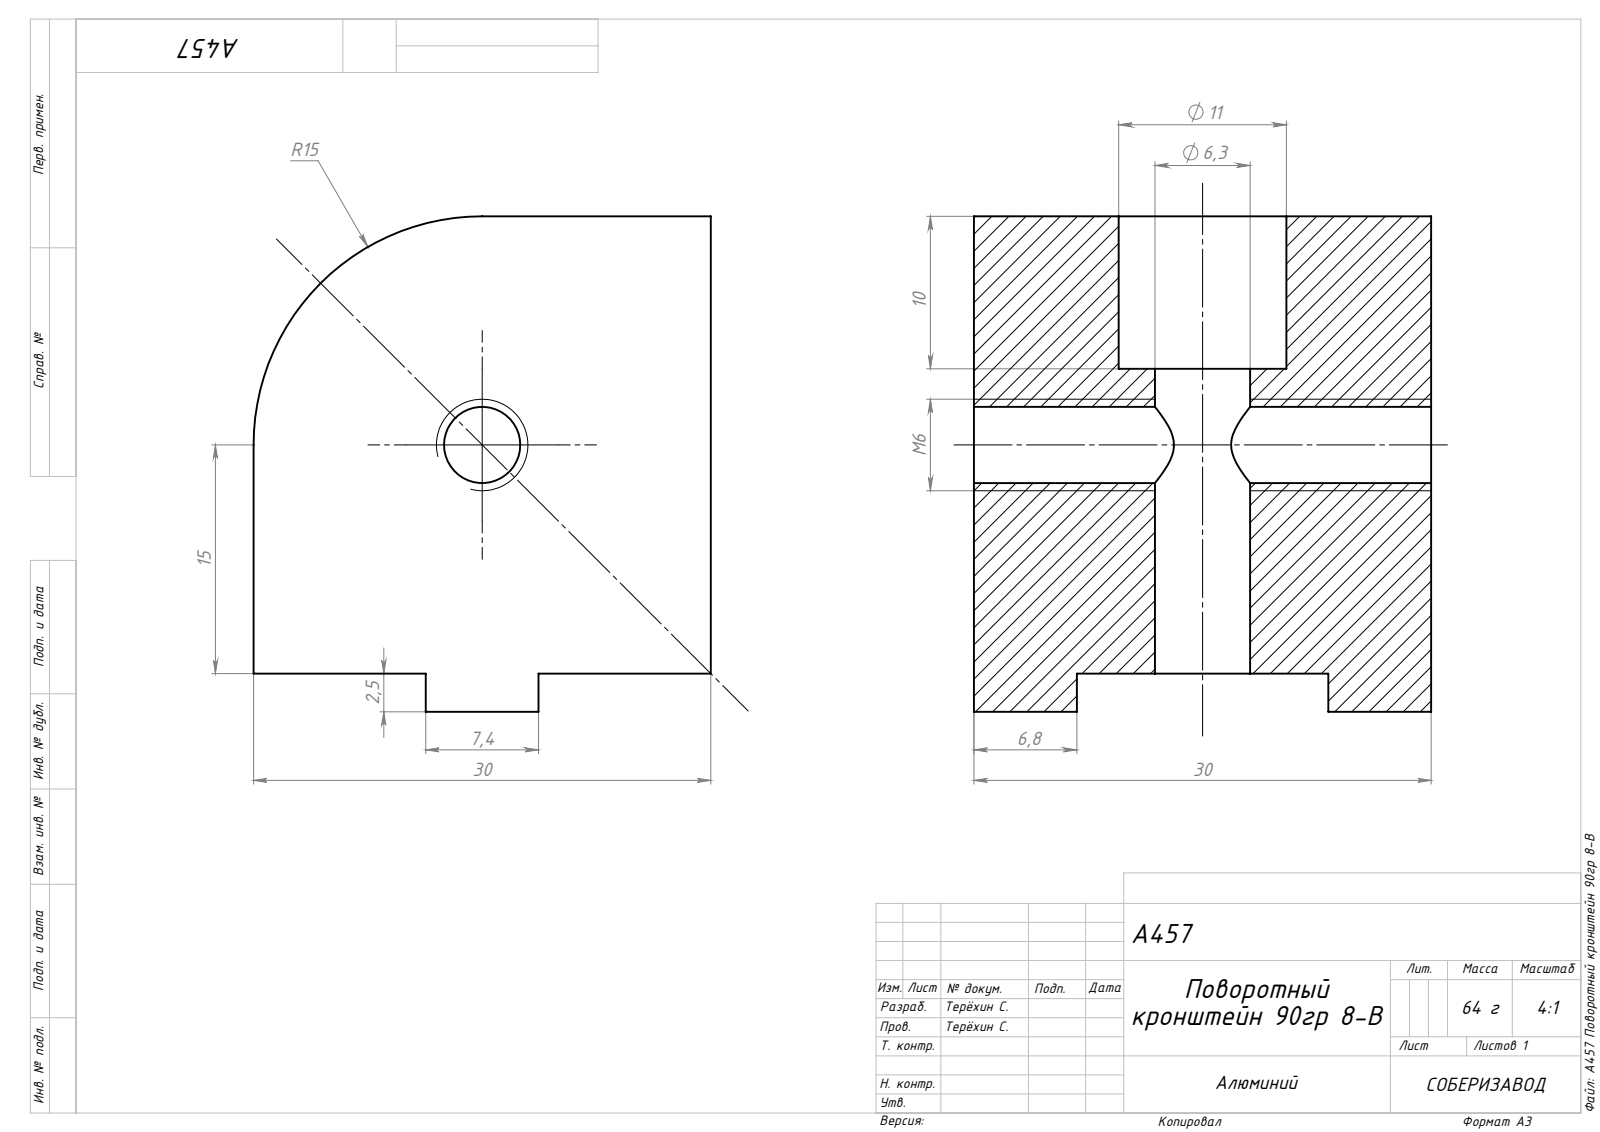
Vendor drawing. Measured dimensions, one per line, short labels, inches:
name: A457 Поворотный кронштейн 90гр 8-B
written by: SolidWorks 2021 (AUTOMOTIVE_DESIGN)
unit: in
bodies: 1 solid, 24 faces (15 planar, 9 cylindrical, 0 other)
size: 1.673 × 1.575 × 1.575
volume: 3.441 in³; area: 16.91 in²
holes: 1× ⌀0.287, 1× ⌀0.325, 1× ⌀0.541
rounds: 1× R0.787
face distances: 1.575, 0.098, 1.673, 1.28, 1.181, 0.394, 0.642, 0.933, 0.266, 1.309
